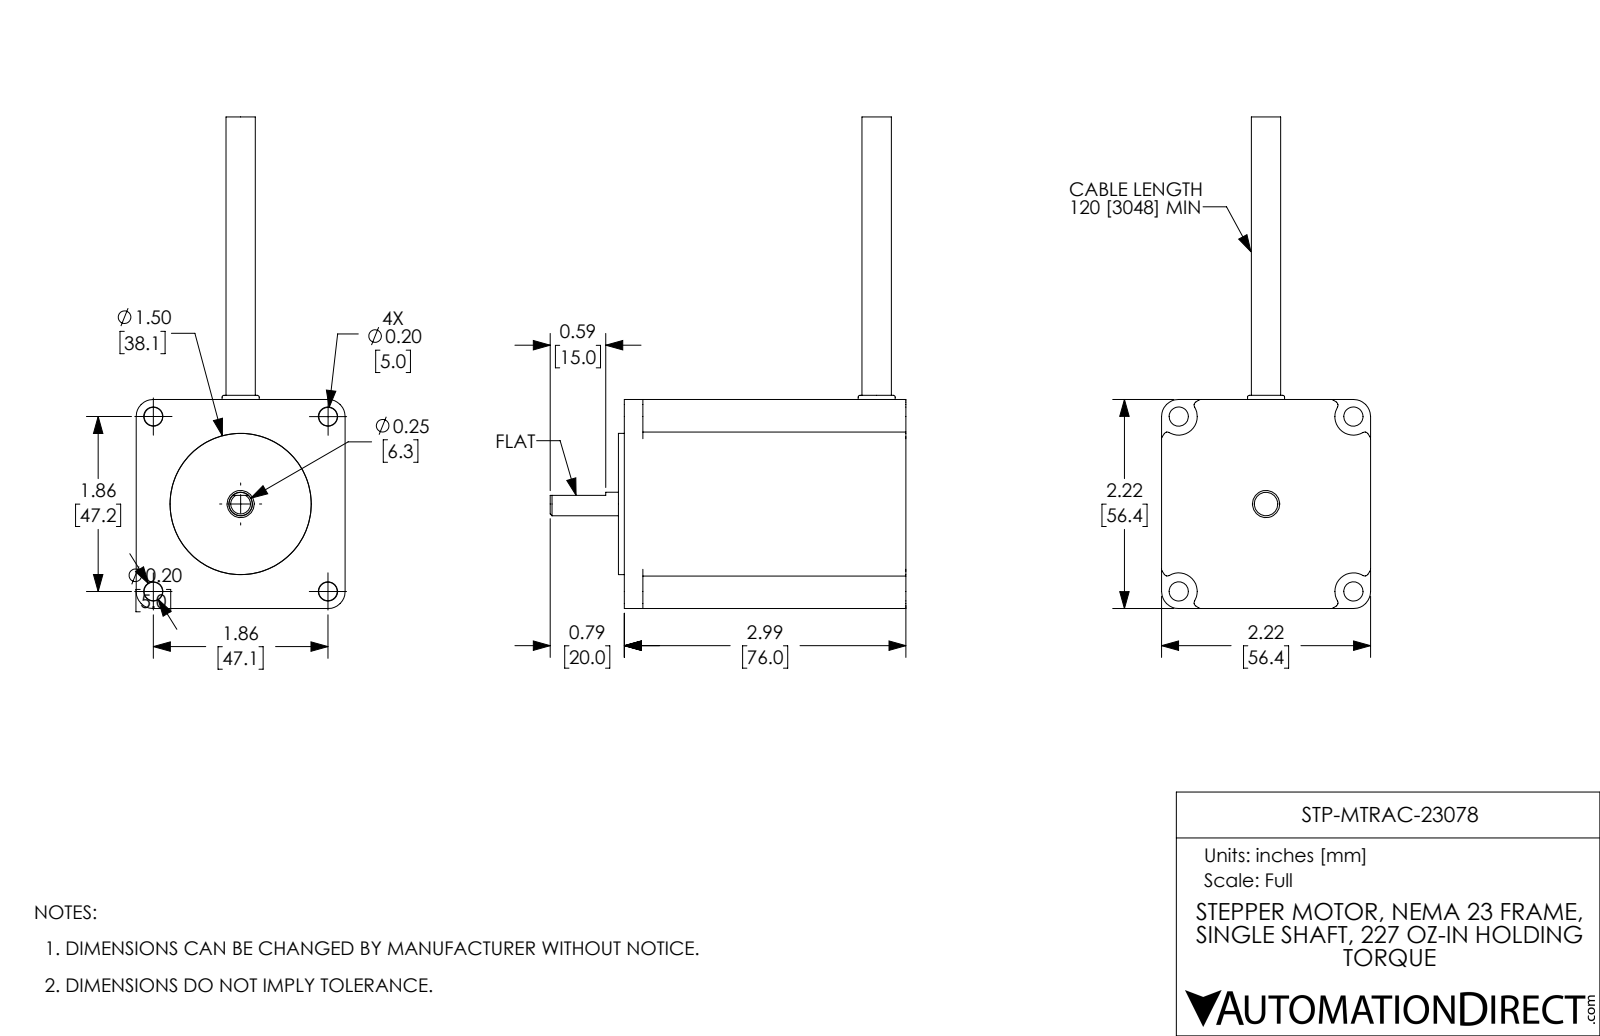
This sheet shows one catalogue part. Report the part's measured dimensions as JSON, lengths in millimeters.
{"part_name": "STP-MTRAC-23078 from HT23-554-CAA New r1", "step_written_by": "SolidWorks 2017 (AUTOMOTIVE_DESIGN)", "units": "millimeters", "bodies": {"solids": 2, "faces": 108, "planar": 21, "cylindrical": 2, "other": 85}, "overall_size": [132.6, 96, 56.4], "volume_mm3": 223400, "surface_area_mm2": 25760, "round_bosses_or_shafts": [[7.9, 1]], "face_to_face_distances": [56.4, 76, 77.6, 1.6, 5, 71, 6.6, 30.5, 25.9, 132.6]}
